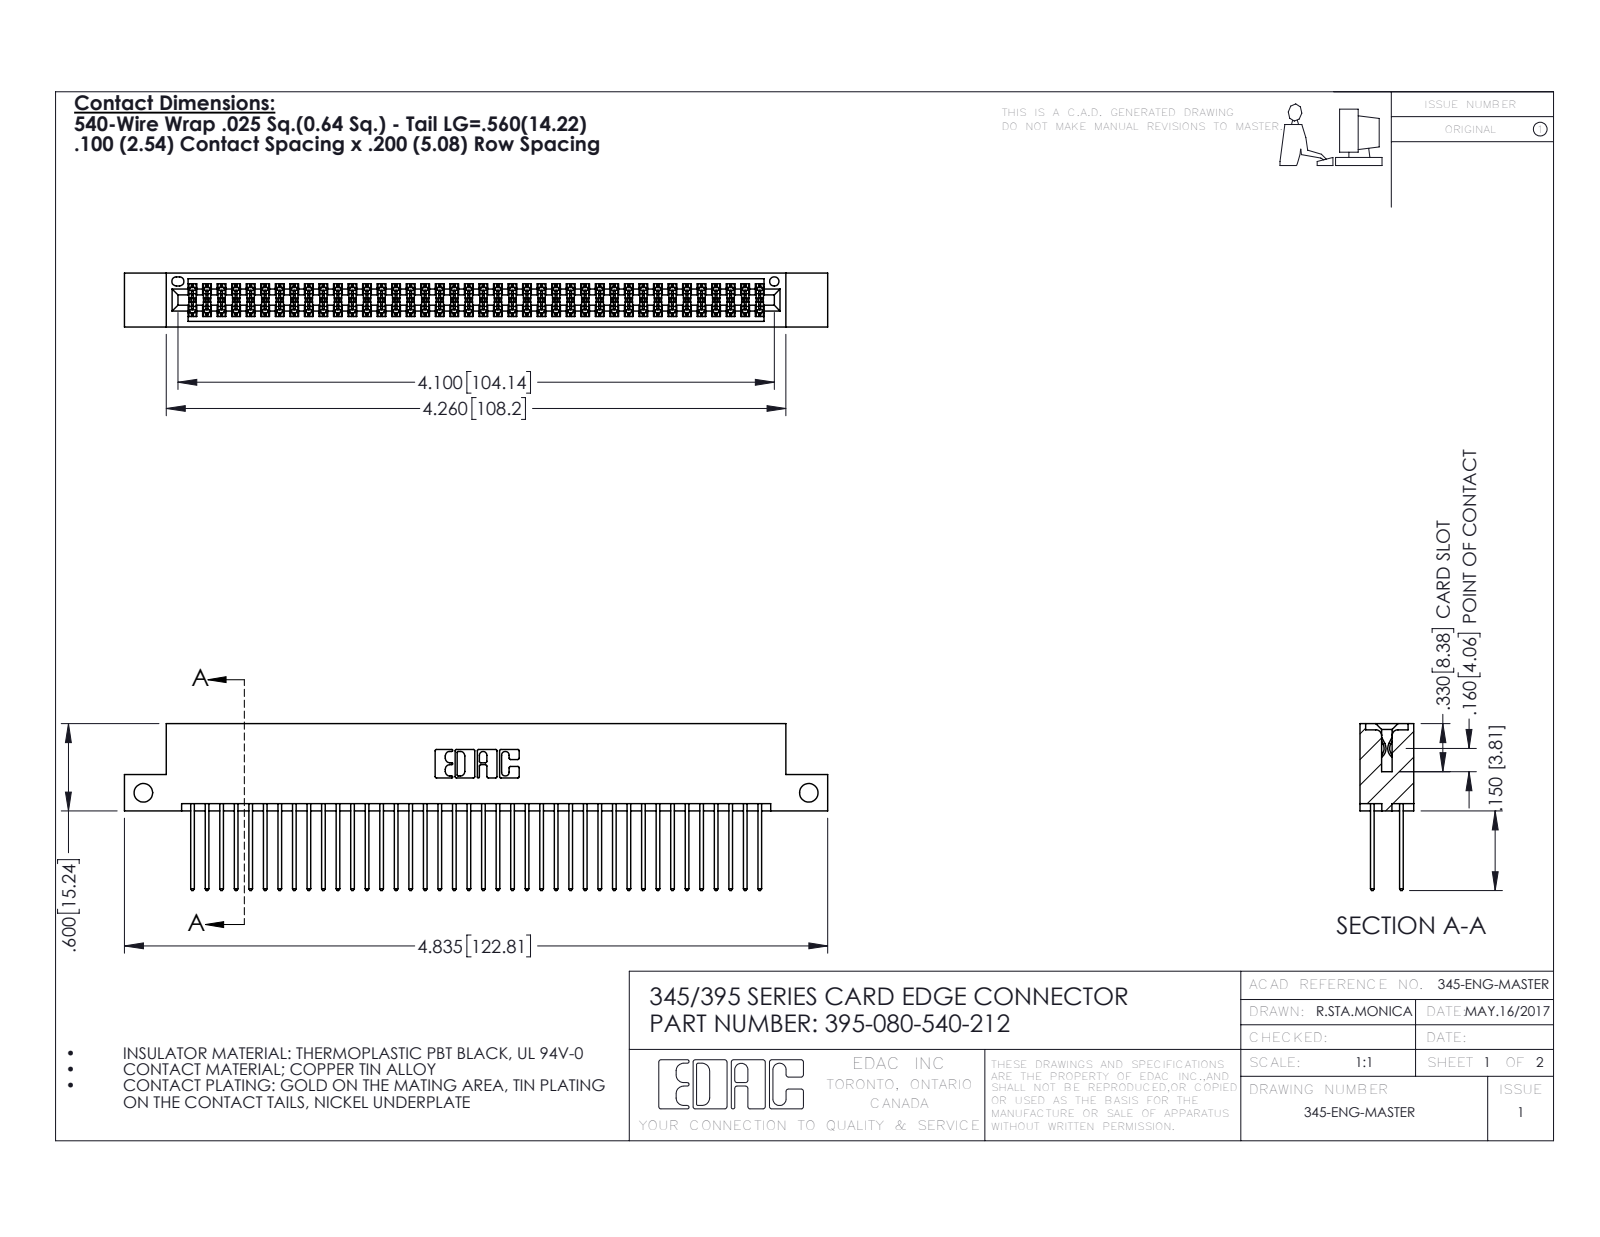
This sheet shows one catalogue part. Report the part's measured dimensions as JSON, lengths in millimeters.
{"part_name": "345-292-001_345-293-140; 345 Part_Flush Mounting Lugs - Side Mount; 395-080-540-212", "step_written_by": "SolidWorks 2016 (CONFIG_CONTROL_DESIGN)", "units": "millimeters", "bodies": {"solids": 81, "faces": 4126, "planar": 2720, "cylindrical": 1406, "other": 0}, "overall_size": [122.8, 29.1, 9.4], "volume_mm3": 12100, "surface_area_mm2": 19160, "round_holes": [[3.3, 2], [1.6, 1]], "partial_cylinders_radius": [[0.2, 120], [0.3, 80], [0.3, 22], [0.2, 6], [0.8, 6], [0.7, 3], [0.4, 2], [0.5, 2]], "face_to_face_distances": [7.6, 1.8, 5.1, 2.5, 6.9, 0.6, 9.4, 5.7, 4.4, 3.8], "hole_center_spacings": [116.2]}
